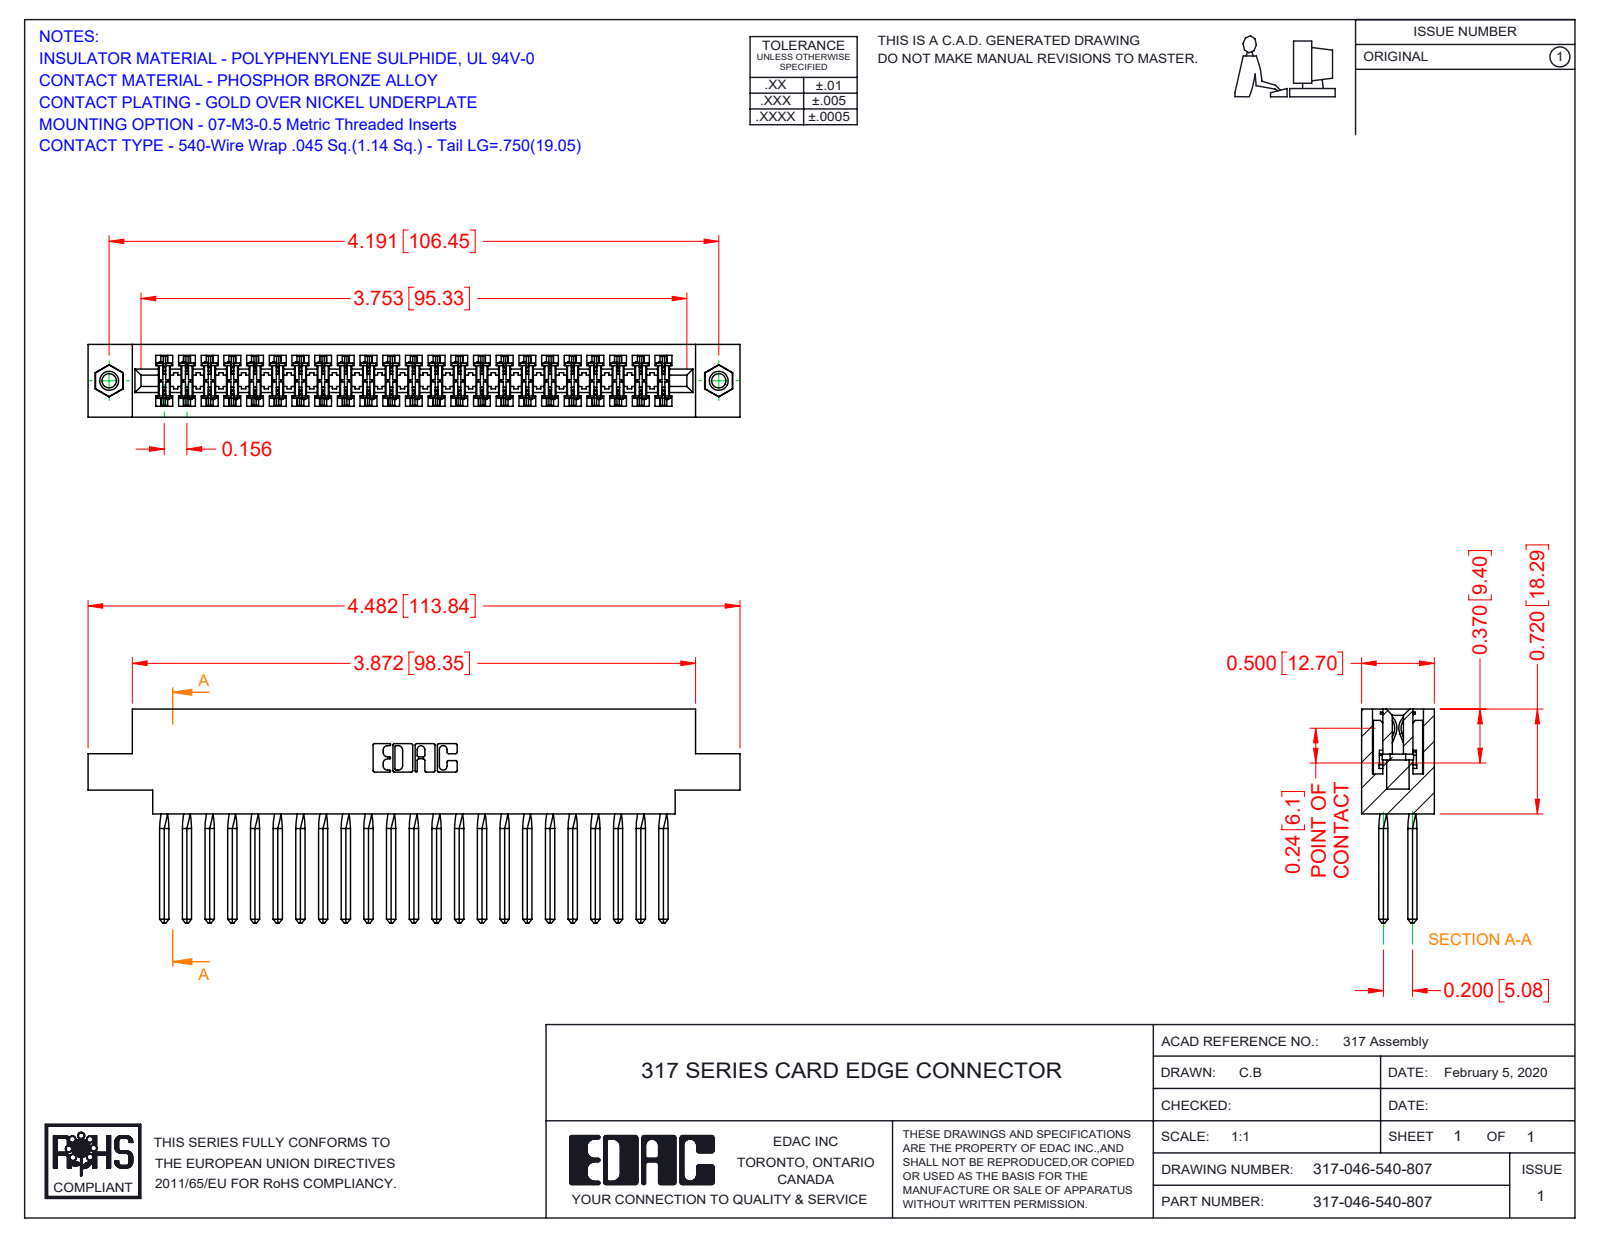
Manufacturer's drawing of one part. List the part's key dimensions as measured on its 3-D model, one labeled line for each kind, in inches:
Part name (STEP PRODUCT): 317-046-540-807; 345-250-001_345-250-005-103; 317-290-001_540; 317 Part_.156 Dia - TI
STEP written by: SolidWorks 2016 (CONFIG_CONTROL_DESIGN)
Units: inches
Bodies: 49 solids, 4256 faces (3448 planar, 608 cylindrical, 200 other)
Overall size (bounding box): 4.482 × 1.47 × 0.5
Volume: 1.126 in³ · Surface area: 41.58 in²
Round holes (diameter × count): ⌀0.098 ×2, ⌀0.125 ×2, ⌀0.156 ×2
Round bosses / shafts (diameter × count): ⌀0.155 ×2
Partial cylindrical surfaces — rounded edges, fillets, slot ends (radius × count): R0.015 ×92, R0.01 ×22, R0.007 ×6, R0.031 ×6, R0.026 ×3, R0.095 ×2, R0.1 ×2, R0.11 ×2
Main face-to-face distances: 0.5, 0.075, 0.425, 0.35, 0.11, 0.195, 0.094, 0.72, 0.2, 0.115
Hole centre spacings: 4.191
